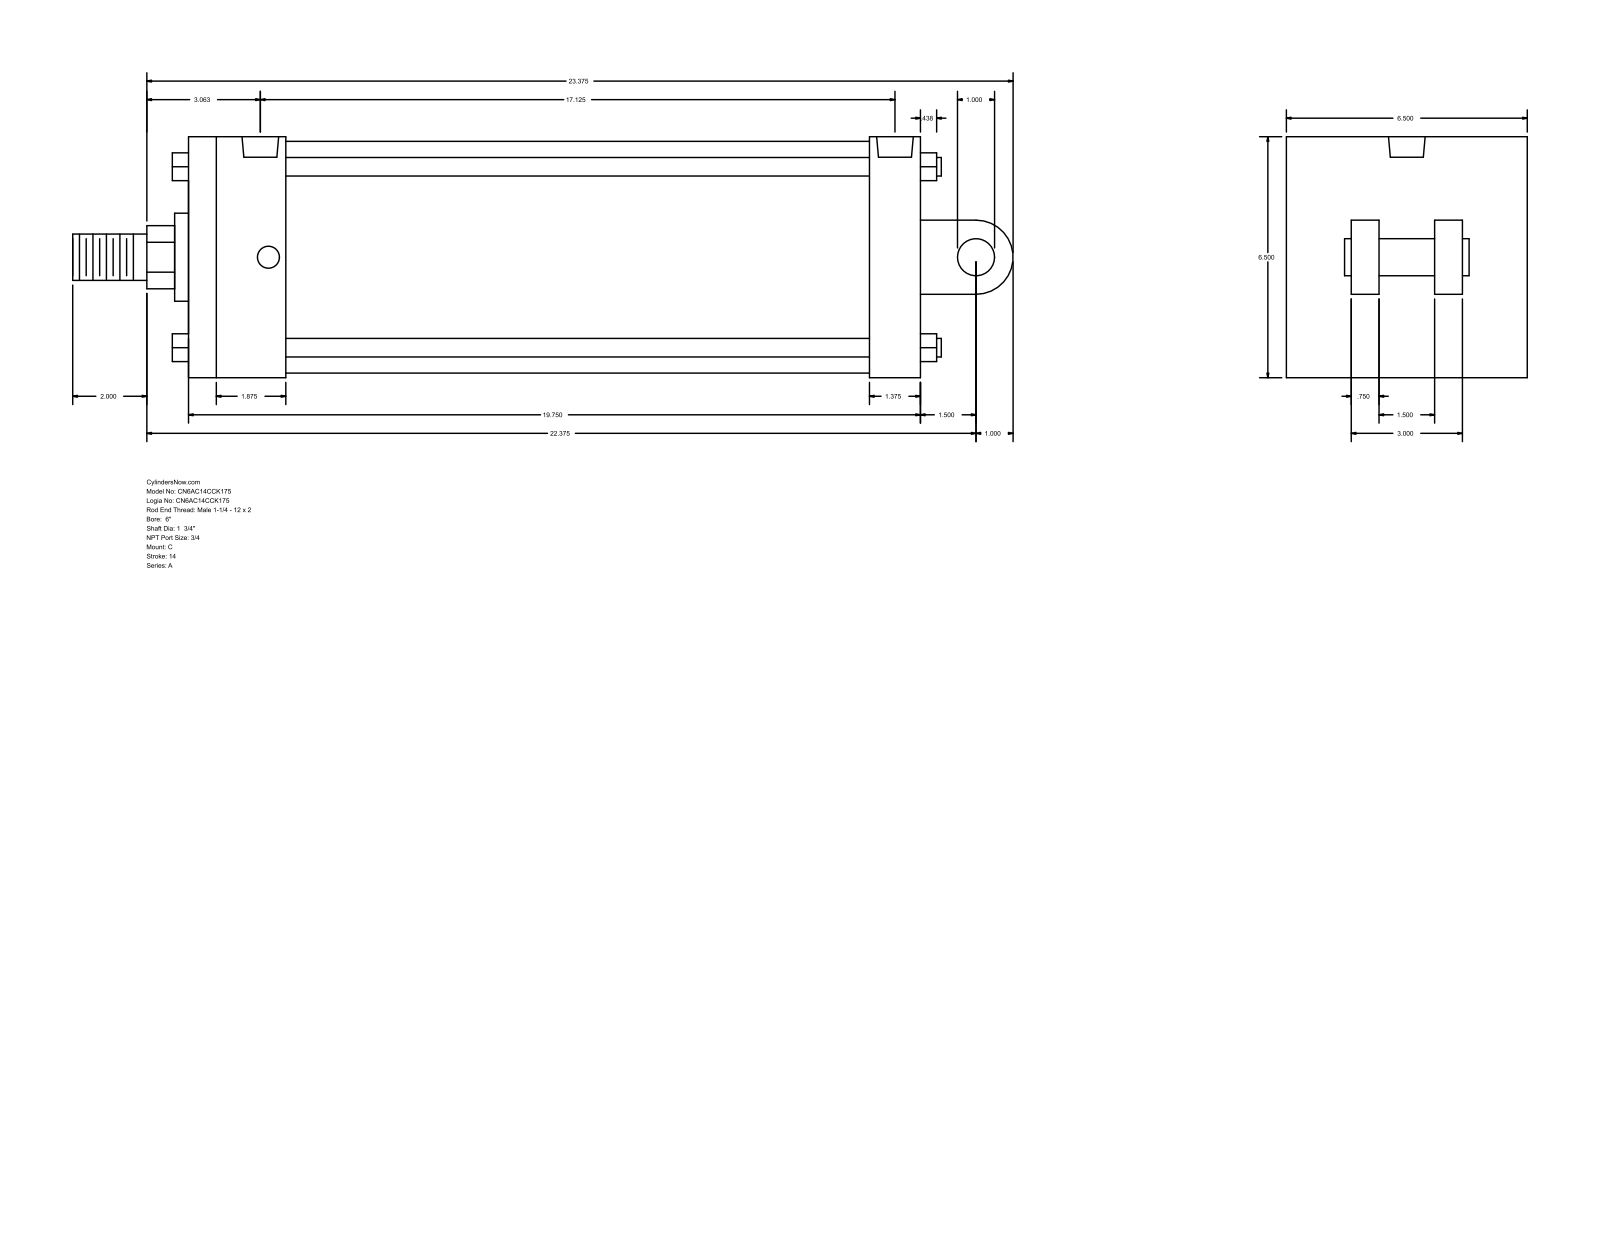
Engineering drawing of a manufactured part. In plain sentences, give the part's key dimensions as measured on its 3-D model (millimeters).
The part is named "A_C__0600_1.75". Its 3-D file was written by "GSSL Pune (CONFIG_CONTROL_DESIGN)". It is 0 solids with 135 faces: 102 planar, 33 cylindrical and 0 other. Overall it measures 644.52 by 165.1 by 165.1 millimeters. Round holes: 4 of diameter 15.08, 2 of diameter 25.12. Round bosses or shafts: 4 of diameter 12.7, 1 of diameter 158.75, 1 of diameter 60.33, 1 of diameter 44.45, 1 of diameter 31.75, 1 of diameter 25.4. Partial cylindrical surfaces (rounded edges, fillets, slot ends): 1 of radius 21.63, 1 of radius 25.4. The main face-to-face distances are 165.1, 501.66, 19.05, 57.15, 66.68, 434.98, 466.73, 400.05, 34.93, 63.5. The hole center spacings are 5.56, 423.85, 429.41, 434.97.
